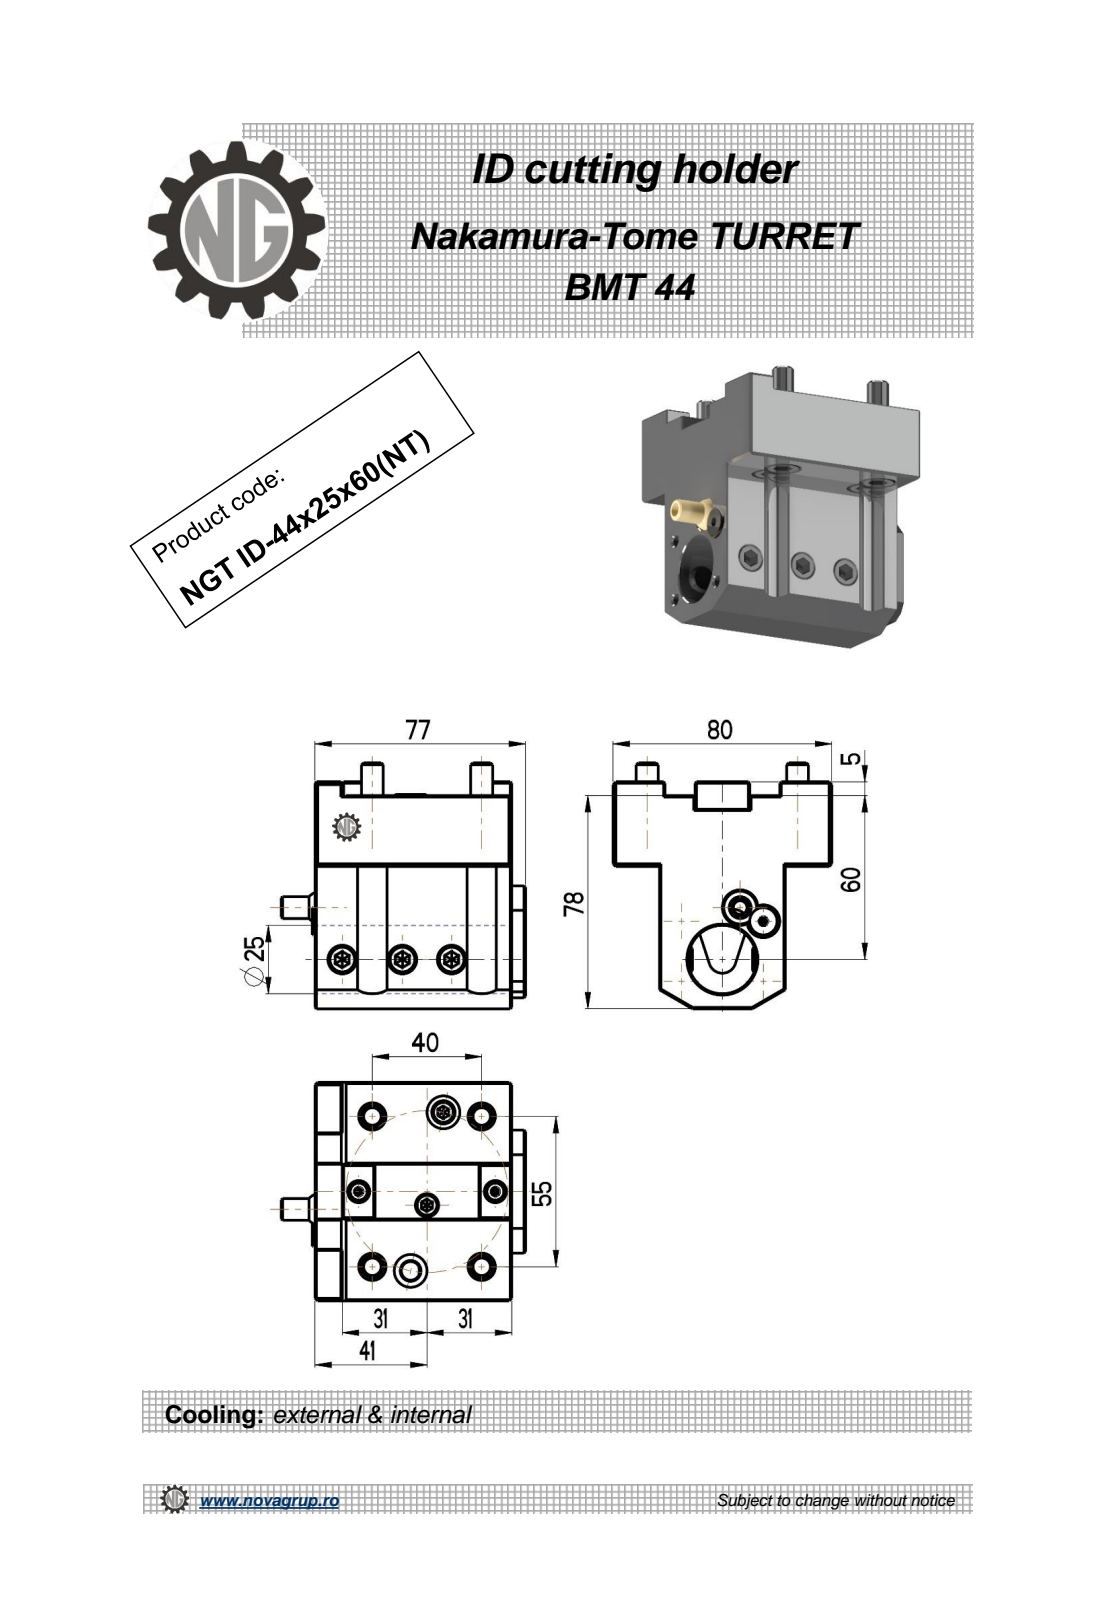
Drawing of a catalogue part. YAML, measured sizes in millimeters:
part_name: "NGT_ID_44_25_60_NT"
step_written_by: "PRO/ENGINEER BY PARAMETRIC TECHNOLOGY CORPORATION, 2010280 (CONFIG_CONTROL_DESIGN)"
units: millimeters
bodies: {solids: 1, faces: 558, planar: 280, cylindrical: 140, other: 138}
overall_size: [90, 89.34, 80]
volume: 283392
surface_area: 49732
round_holes:
  - {diameter: 9, count: 4}
  - {diameter: 14, count: 4}
  - {diameter: 12, count: 2}
  - {diameter: 5, count: 1}
  - {diameter: 6.8, count: 1}
  - {diameter: 25, count: 1}
round_bosses_or_shafts:
  - {diameter: 8, count: 5}
  - {diameter: 13, count: 4}
  - {diameter: 10, count: 4}
partial_cylinders:
  - {radius: 0.51, count: 36}
  - {radius: 0.26, count: 20}
  - {radius: 0.2, count: 6}
  - {radius: 0.41, count: 6}
  - {radius: 5, count: 3}
  - {radius: 10, count: 2}
face_to_face_distances: [17, 63, 5, 72, 46, 26, 80, 52, 77, 78]
hole_center_spacings: [14.08, 26.04, 40, 55, 58.21, 62.2, 68.01, 20.08]
